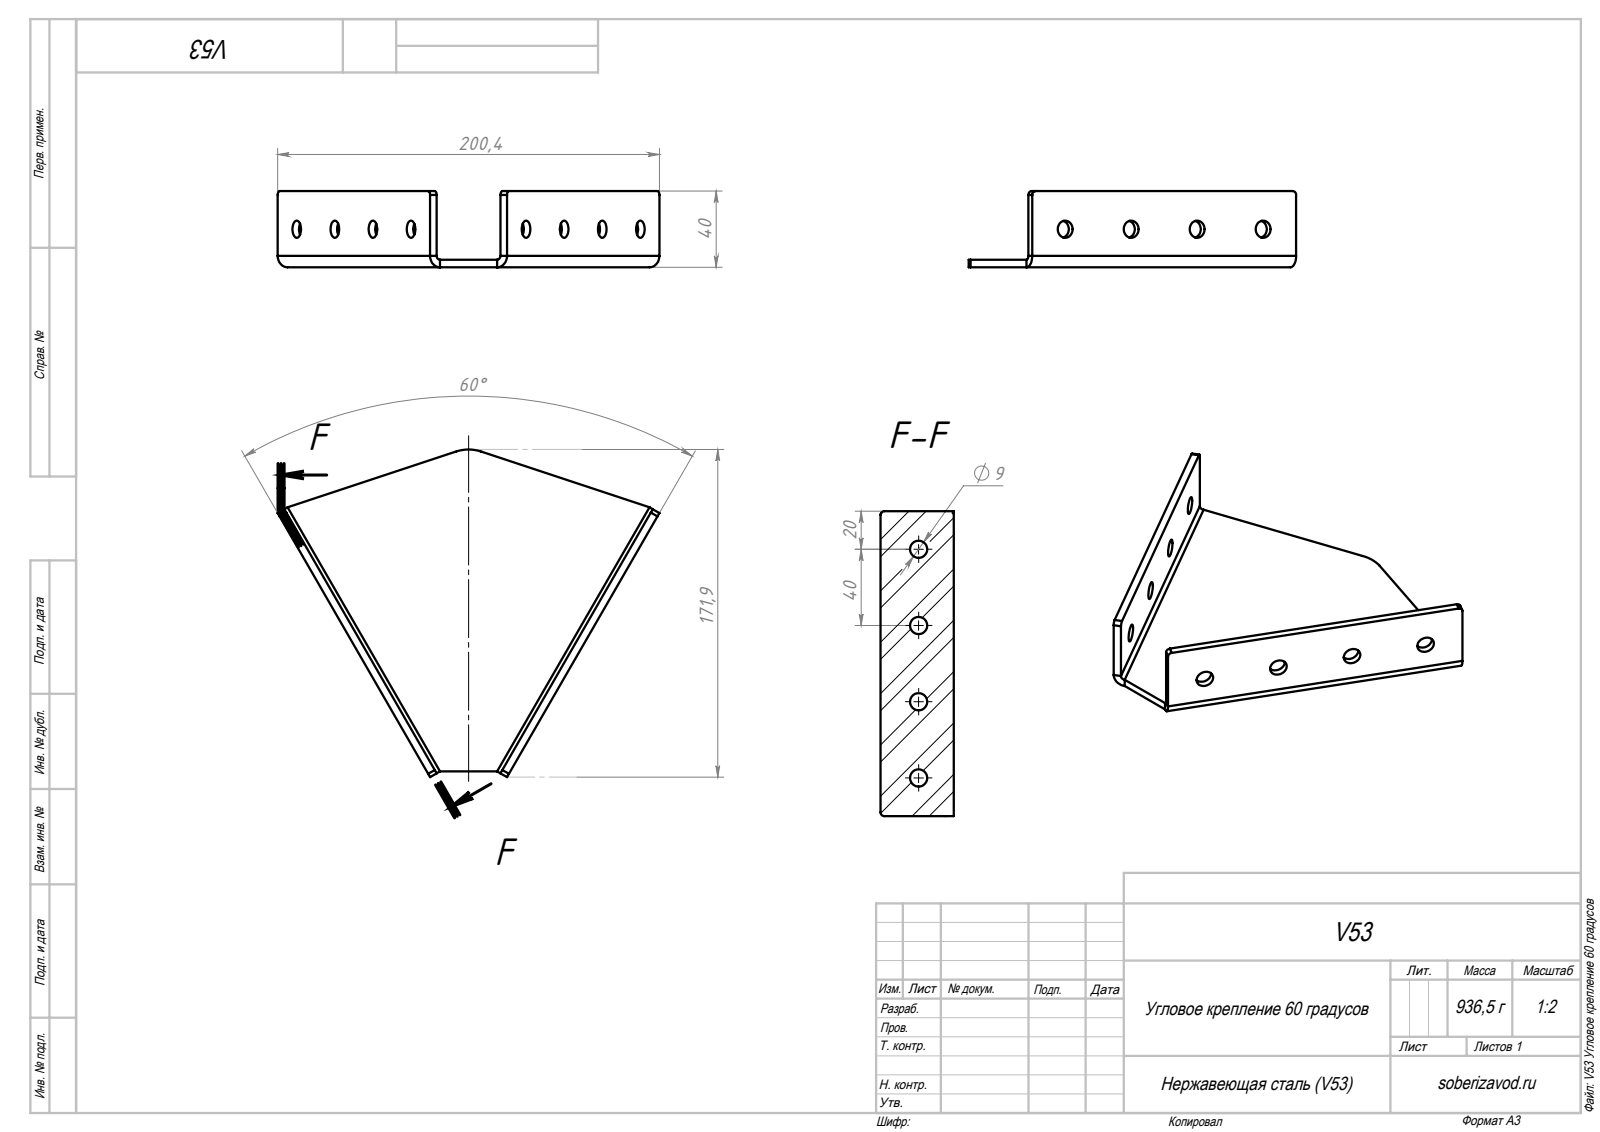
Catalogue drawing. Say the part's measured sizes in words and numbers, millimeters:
The part is named "V53 Угловое крепление 60 градусов". Its 3-D file was written by "SolidWorks 2018 (AUTOMOTIVE_DESIGN)". It is 1 solid with 44 faces: 19 planar, 25 cylindrical and 0 other. Overall it measures 200.39 by 171.93 by 40 millimeters. Its volume is 122 409 cubic millimeters and its surface area 64 939 square millimeters. Round holes: 8 of diameter 9. Partial cylindrical surfaces (rounded edges, fillets, slot ends): 6 of radius 2, 2 of radius 6, 1 of radius 20. The main face-to-face distances are 4, 40, 36, 160. The hole center spacings are 40, 80, 120.
